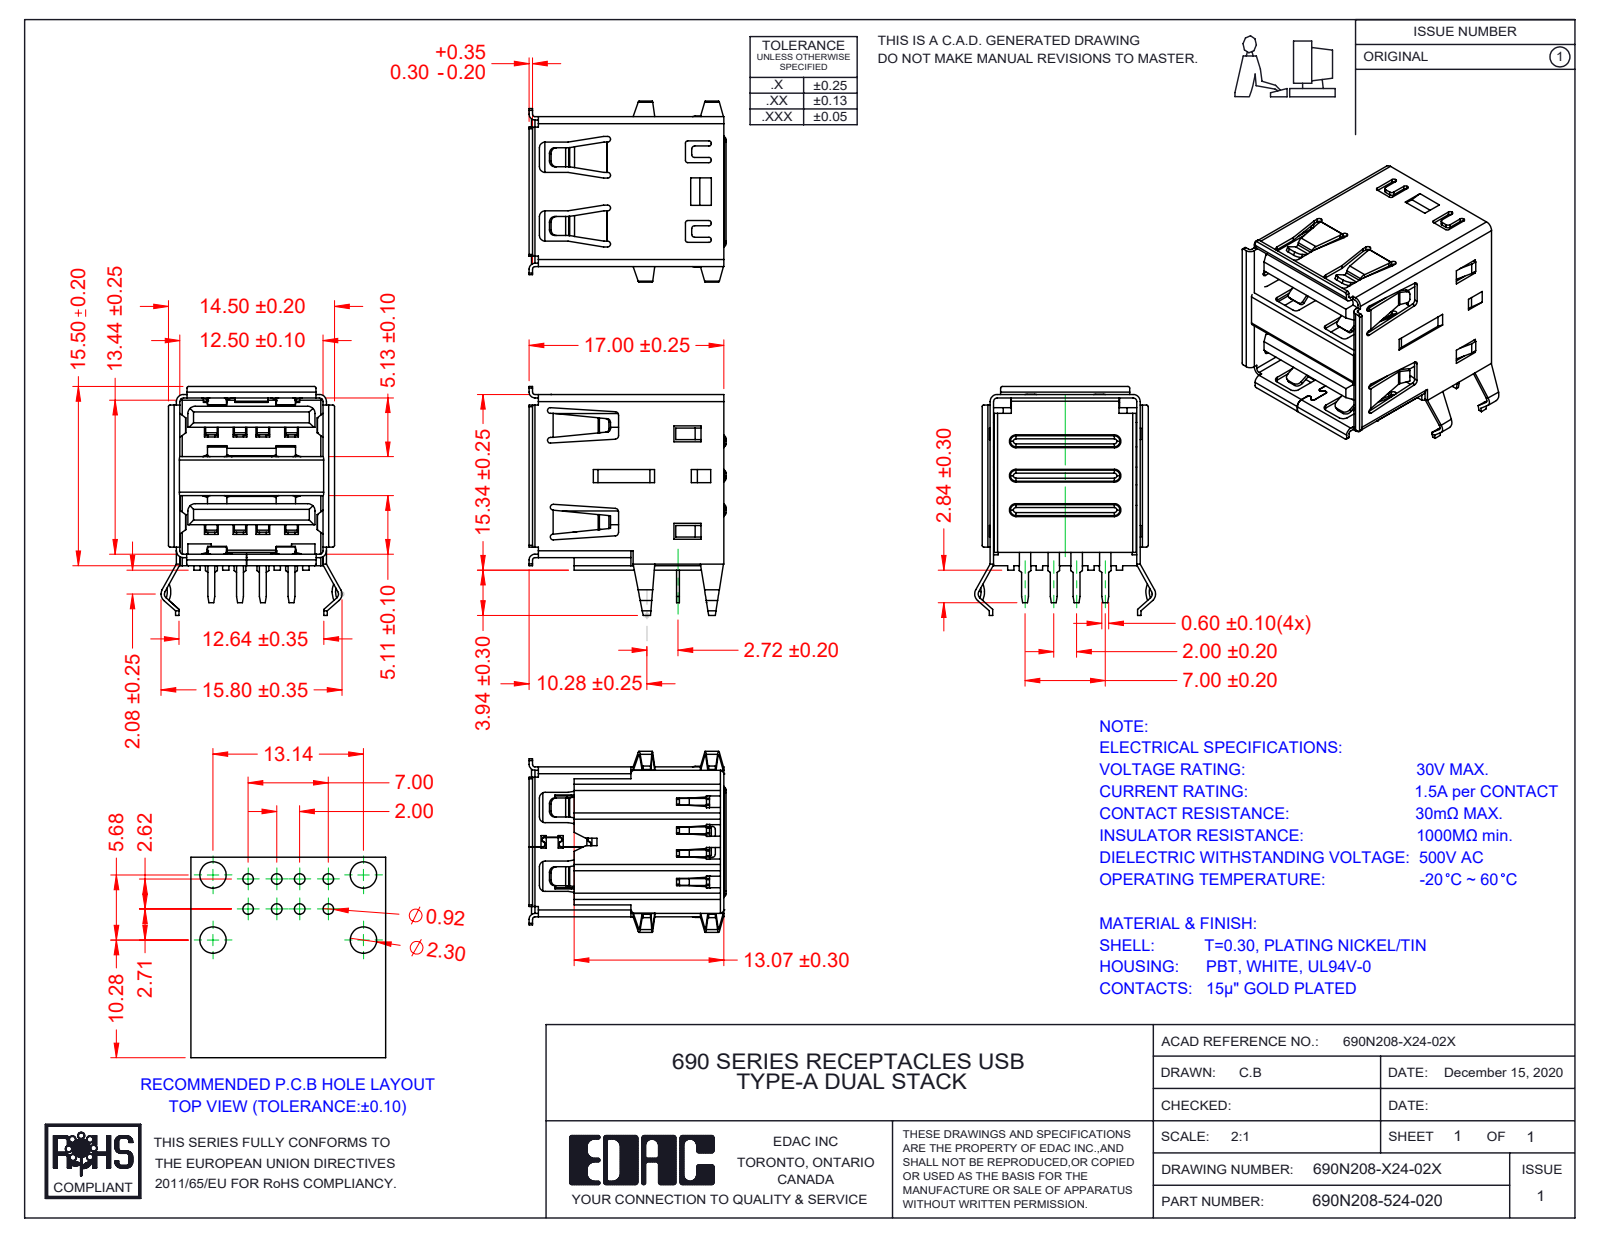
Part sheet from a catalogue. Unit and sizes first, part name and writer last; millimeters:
Units: millimetres
Overall size (bounding box): 19.98 × 17.2 × 15.8
Partial cylindrical surfaces — rounded edges, fillets, slot ends (radius × count): R0.25 ×39, R0.2 ×31, R0.5 ×25, R0.3 ×23, R0.1 ×14, R0.15 ×9, R0.4 ×7, R0.18 ×4
Main face-to-face distances: 12.8, 0.7, 12.5, 8.5, 4.5, 5.41, 2.5, 1, 13.1, 13.94
Volume: 1 554 mm³ · Surface area: 5 527 mm²
Bodies: 11 solids, 1766 faces (1394 planar, 329 cylindrical, 43 other)
Part name (STEP PRODUCT): Contact Upper 690N208-X24-02X; Insulator 690N208-X24-02X; Shell 690N208-X24-02X; Contact Lower 690N208-X24-02X (+2 more)
STEP written by: SolidWorks 2020 (AUTOMOTIVE_DESIGN)
